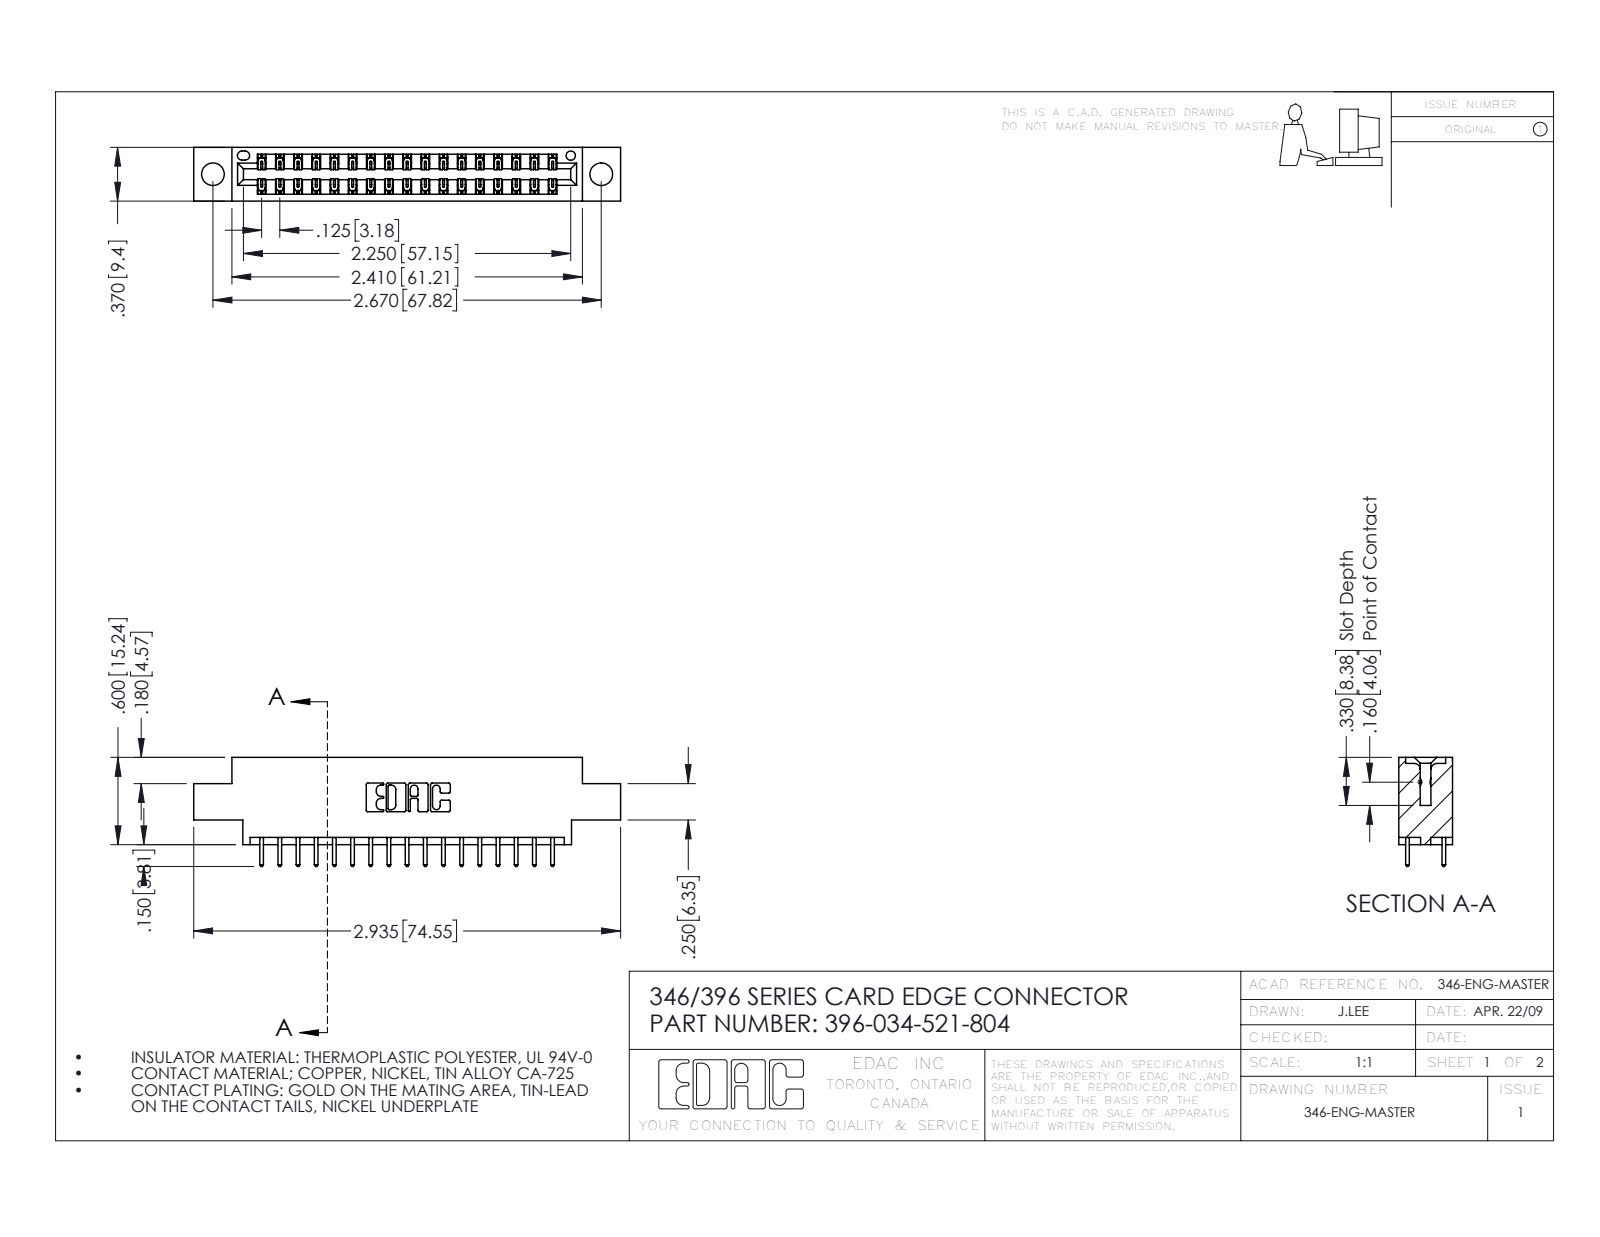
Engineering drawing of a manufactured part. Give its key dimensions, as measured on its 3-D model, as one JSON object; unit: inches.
{"part_name": "396-034-521-804; 346 Part_0.170 Offset - 0.156 Dia-TH; 345-292-001_345-293-121", "step_written_by": "SolidWorks 2016 (CONFIG_CONTROL_DESIGN)", "units": "inches", "bodies": {"solids": 35, "faces": 1894, "planar": 1270, "cylindrical": 624, "other": 0}, "overall_size": [2.935, 0.75, 0.37], "volume_in3": 0.416, "surface_area_in2": 13.76, "round_holes": [[0.156, 2], [0.064, 1]], "partial_cylinders_radius": [[0.006, 51], [0.01, 34], [0.01, 22], [0.007, 6], [0.031, 6], [0.026, 3], [0.014, 2], [0.022, 2]], "face_to_face_distances": [0.048, 0.322, 0.25, 0.37, 0.072, 0.298, 0.025, 0.275, 0.148, 0.222], "hole_center_spacings": [0.246, 2.463, 2.67]}
